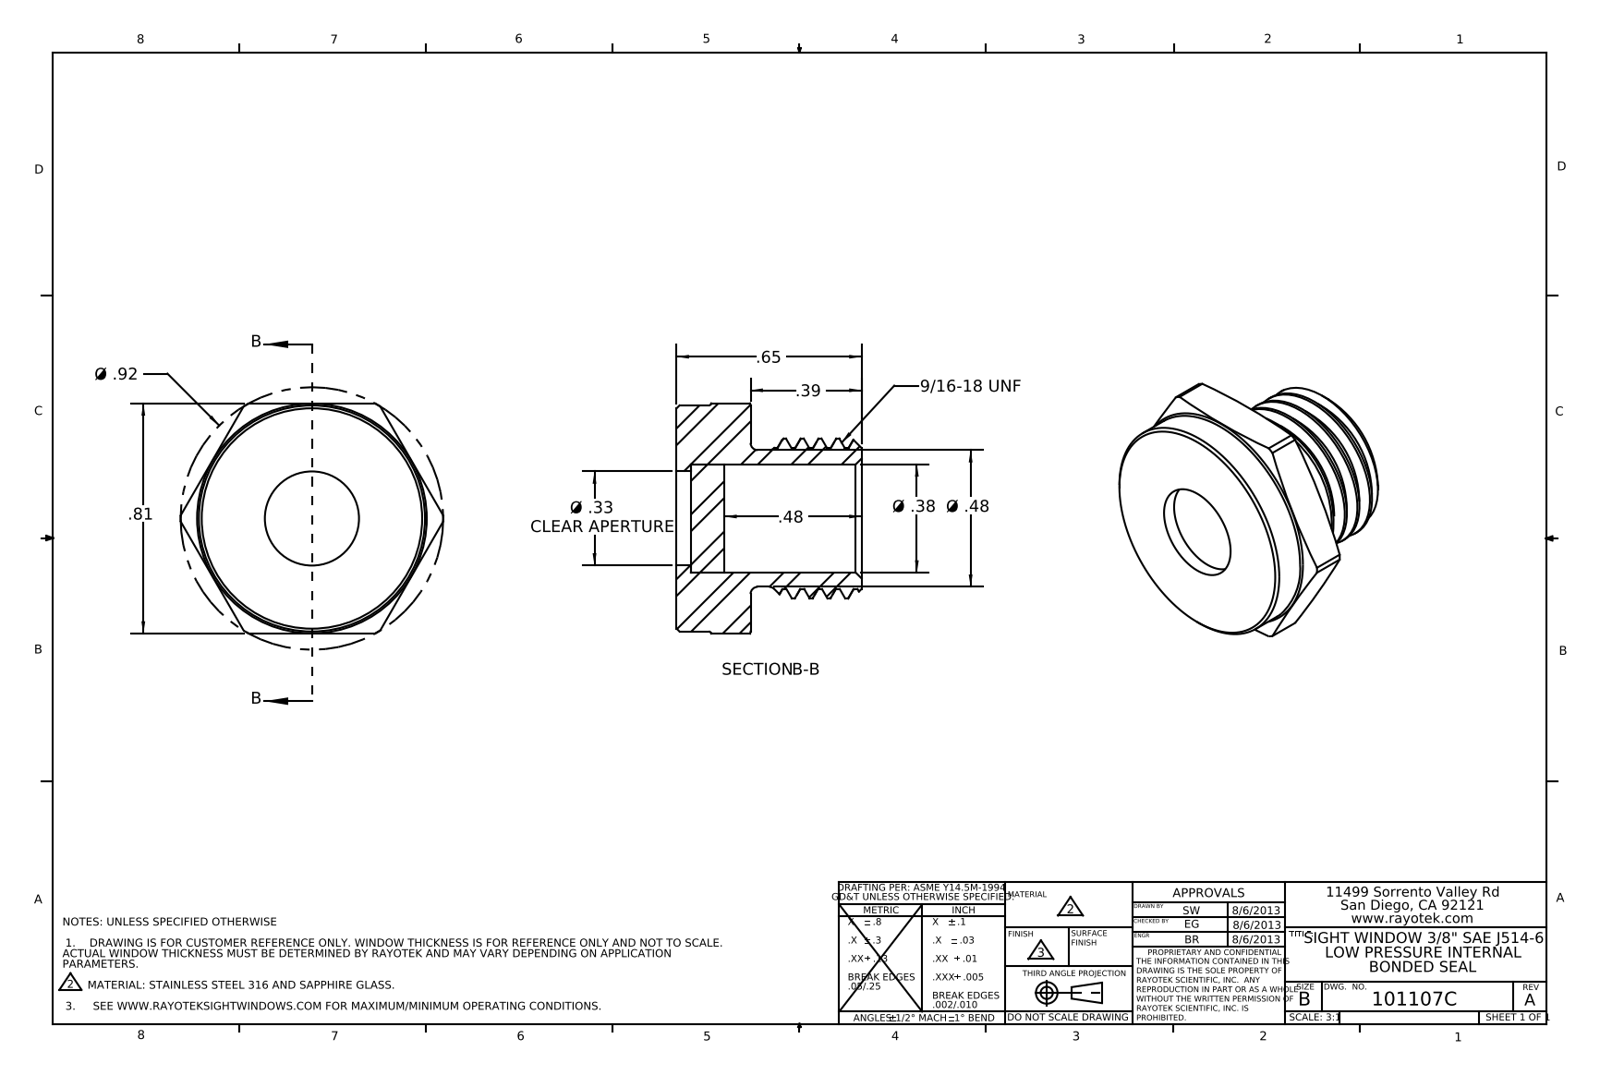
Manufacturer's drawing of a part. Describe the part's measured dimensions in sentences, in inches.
The part is named "403107". Its 3-D file was written by "SolidWorks 2012 (AUTOMOTIVE_DESIGN)". It is 2 solids with 60 faces: 12 planar, 26 cylindrical and 22 other. Overall it measures 0.923 by 0.81 by 0.65 inches. Its volume is 0.161 cubic inches and its surface area 3.657 square inches. Round holes: 1 of diameter 0.331, 1 of diameter 0.381. Round bosses or shafts: 1 of diameter 0.795, 1 of diameter 0.563, 1 of diameter 0.481. Partial cylindrical surfaces (rounded edges, fillets, slot ends): 1 of radius 0.462. The main face-to-face distances are 0.26, 0.81, 0.21, 0.05, 0.092, 0.118, 0.168, 0.39, 0.482, 0.6.
